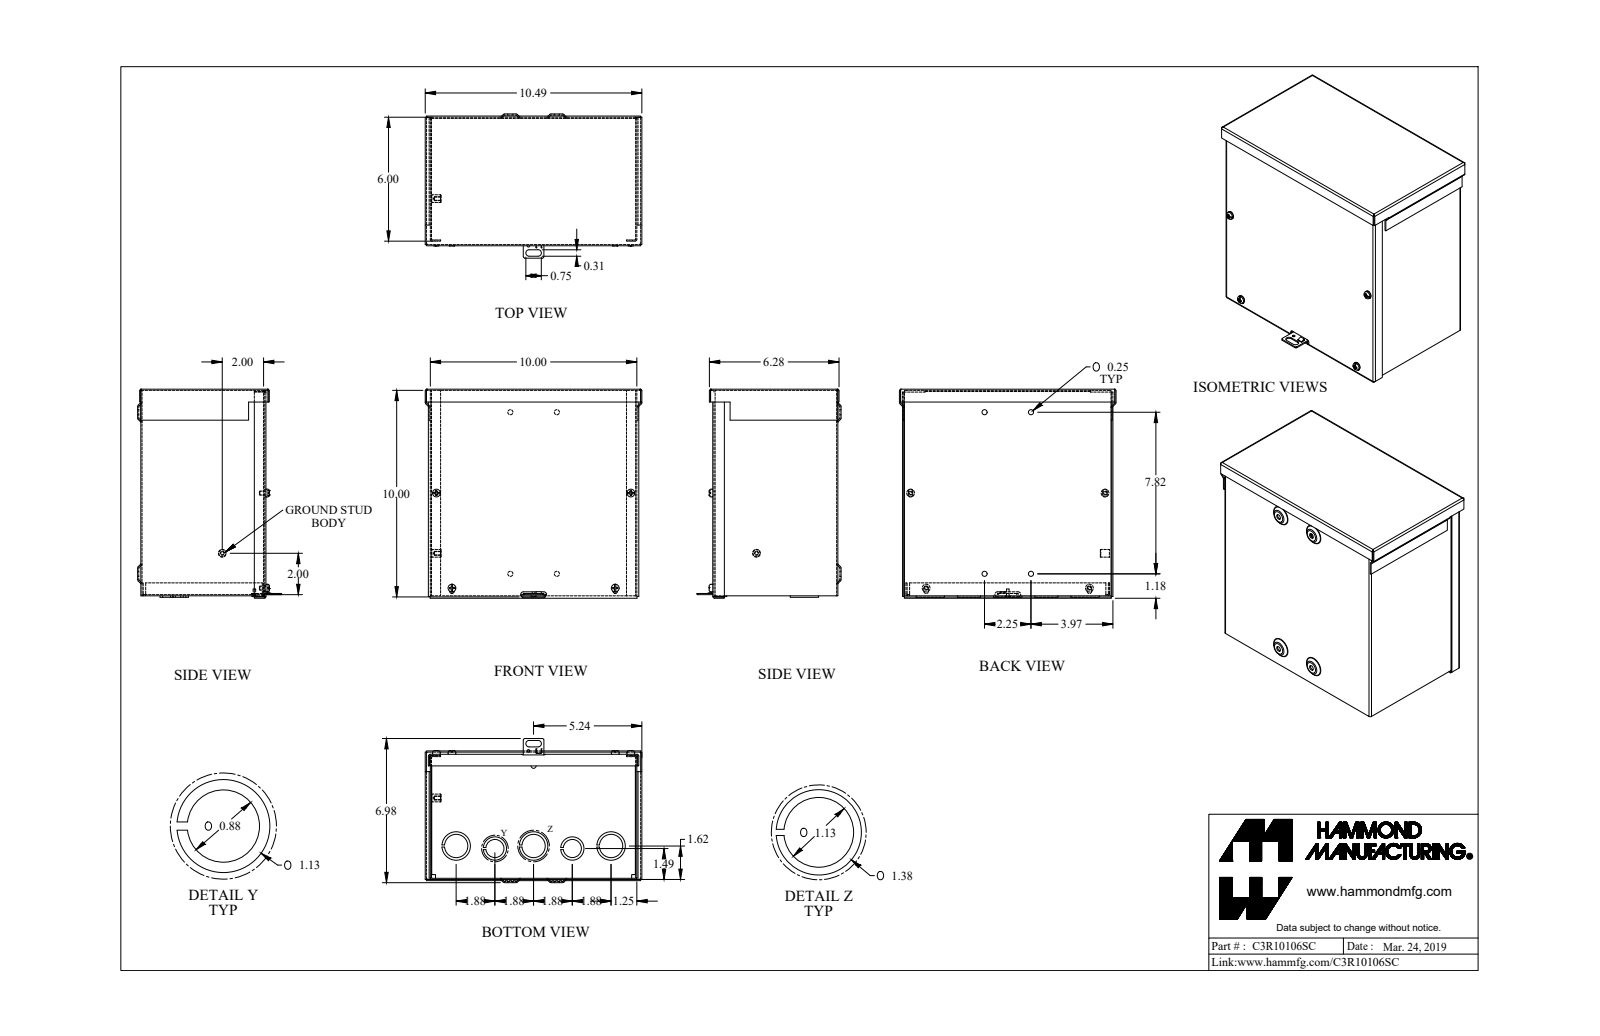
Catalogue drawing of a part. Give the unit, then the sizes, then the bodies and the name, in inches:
Units: inches
Overall size (bounding box): 10.489 × 10.12 × 6.977
Round holes (diameter × count): ⌀0.17 ×4, ⌀0.25 ×4, ⌀1.125 ×3, ⌀0.875 ×2, ⌀0.125 ×1, ⌀0.137 ×1, ⌀0.156 ×1
Round bosses / shafts (diameter × count): ⌀0.375 ×4, ⌀0.19 ×4, ⌀1.375 ×2, ⌀1.125 ×2, ⌀1.375 ×1, ⌀0.375 ×1, ⌀0.125 ×1
Partial cylindrical surfaces — rounded edges, fillets, slot ends (radius × count): R0.029 ×21, R0.086 ×21, R0.109 ×8, R0.125 ×8, R0.156 ×2
Main face-to-face distances: 0.057, 6, 9.943, 10, 5.943, 6.057, 0.057, 9.886, 9.886, 9.943
Hole centre spacings: 5.302, 7.021, 3.75, 1.879, 1.88, 2.25, 2.946, 4.736
Volume: 29.56 in³ · Surface area: 1 045 in²
Bodies: 11 solids, 429 faces (226 planar, 117 cylindrical, 86 other)
Part name (STEP PRODUCT): C3R10106SC_Default
STEP written by: SolidWorks 2019 (CONFIG_CONTROL_DESIGN)
